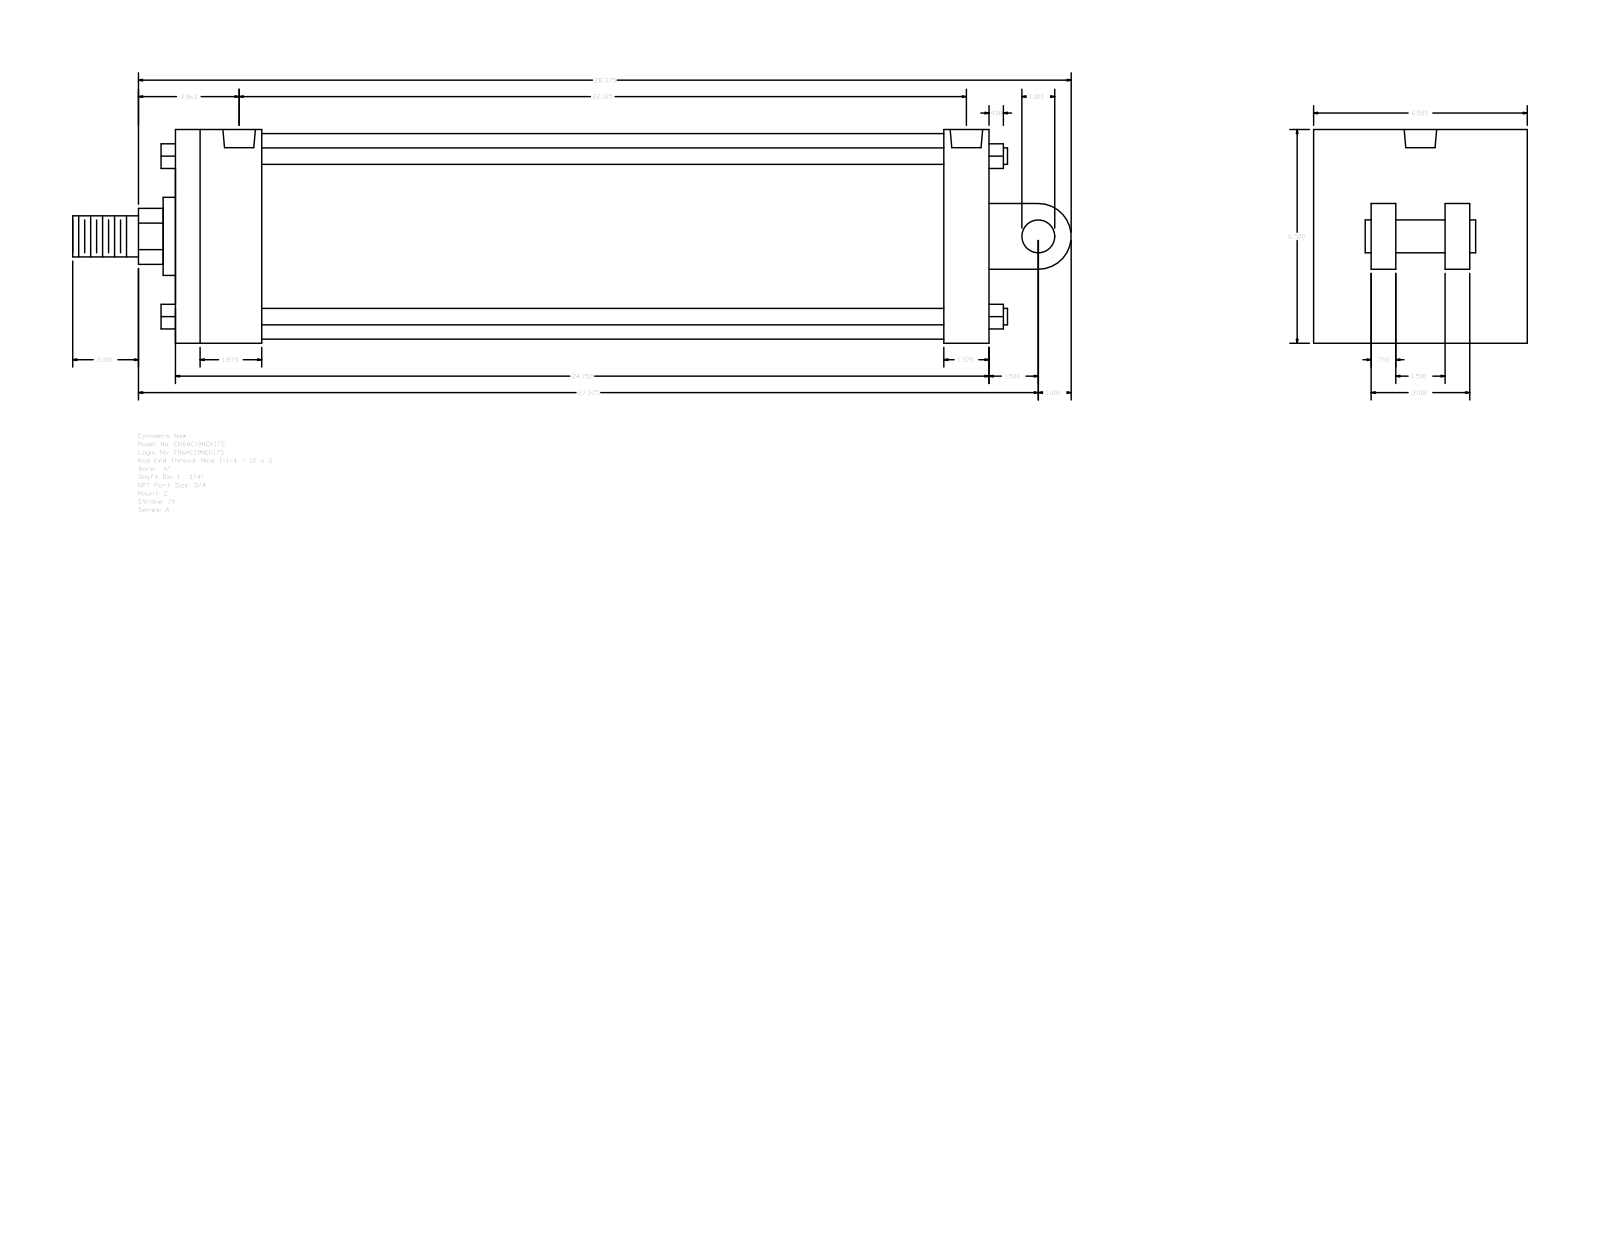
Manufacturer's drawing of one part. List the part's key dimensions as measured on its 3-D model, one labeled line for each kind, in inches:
Part name (STEP PRODUCT): A_C__0600_1.75
STEP written by: GSSL Pune (CONFIG_CONTROL_DESIGN)
Units: inches
Bodies: 0 solids, 135 faces (102 planar, 33 cylindrical, 0 other)
Overall size (bounding box): 30.375 × 6.5 × 6.5
Round holes (diameter × count): ⌀0.594 ×4, ⌀0.989 ×2
Round bosses / shafts (diameter × count): ⌀0.5 ×4, ⌀6.25 ×1, ⌀2.375 ×1, ⌀1.75 ×1, ⌀1.25 ×1, ⌀1 ×1
Partial cylindrical surfaces — rounded edges, fillets, slot ends (radius × count): R0.852 ×1, R1 ×1
Main face-to-face distances: 6.5, 24.75, 0.75, 2.25, 2.625, 22.125, 23.375, 20.75, 1.375, 2.5
Hole centre spacings: 0.219, 21.687, 21.906, 22.125
